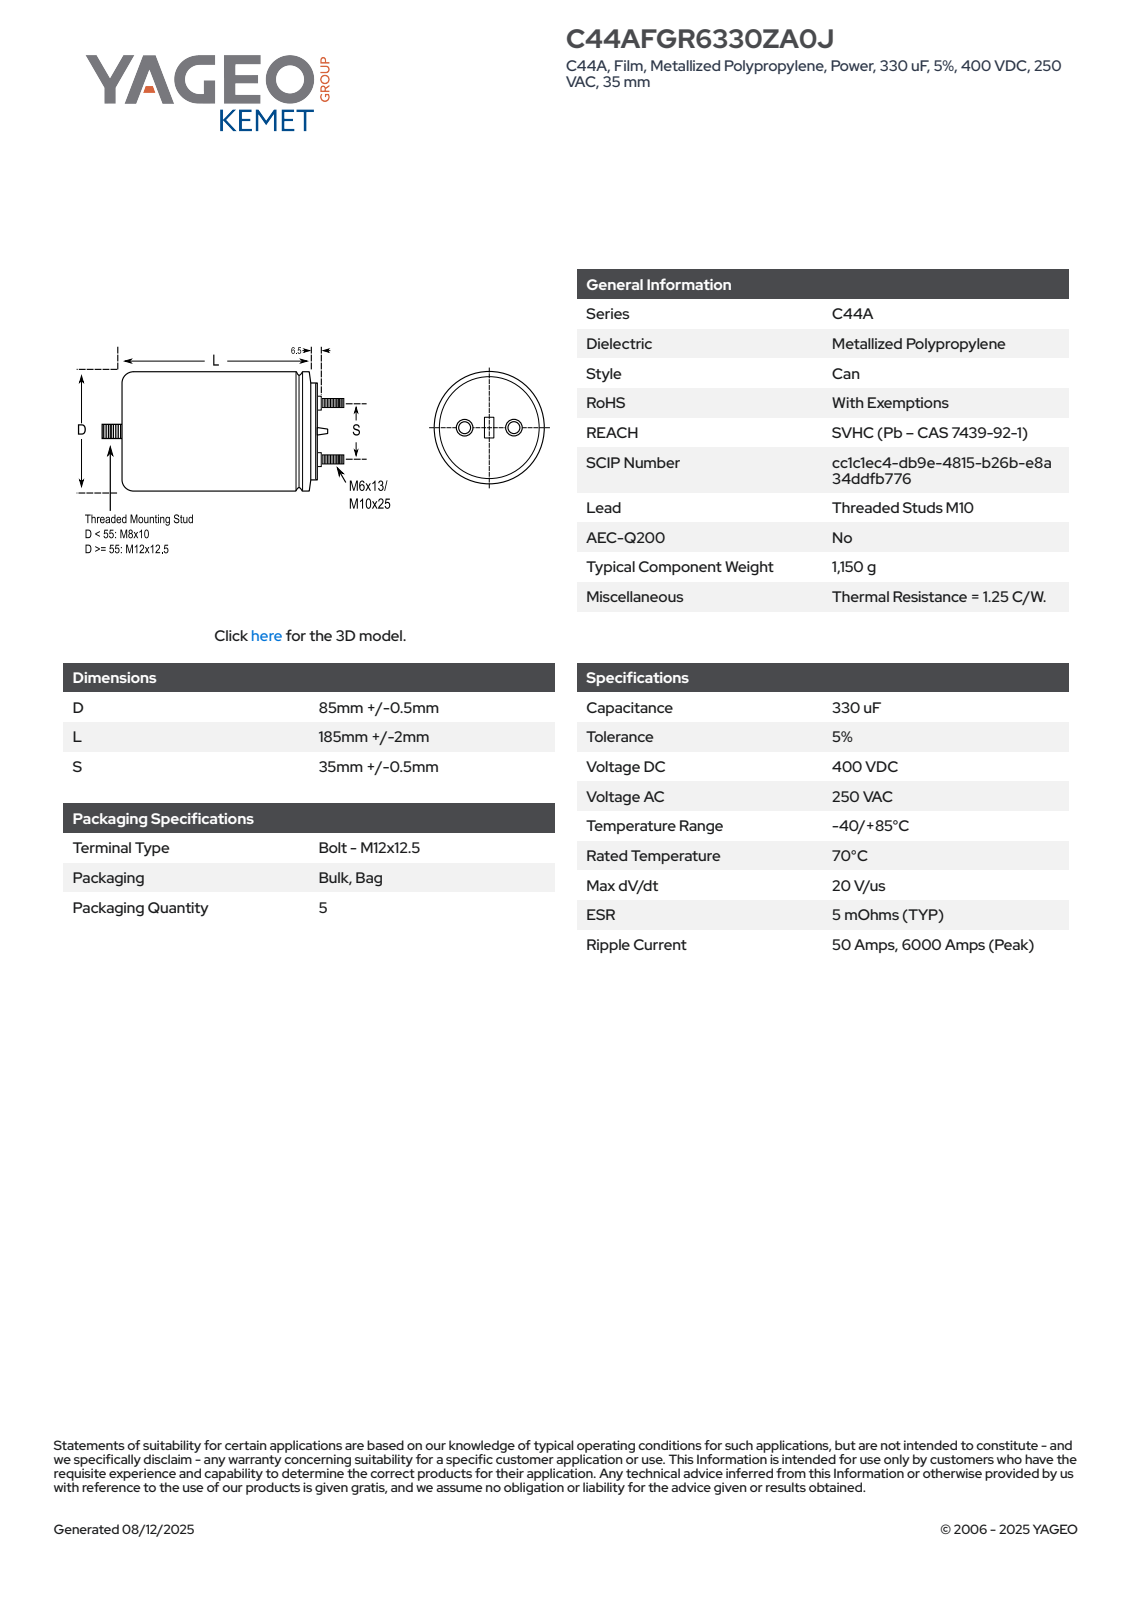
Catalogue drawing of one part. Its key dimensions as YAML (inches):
part_name: "CFP_C44A_85X185_D85.5L187S35"
step_written_by: "SolidWorks 2014 (AUTOMOTIVE_DESIGN)"
units: inches
bodies: {solids: 1, faces: 102, planar: 29, cylindrical: 34, other: 39}
overall_size: [8.622, 3.366, 3.366]
volume: 66.21
surface_area: 97.78
round_bosses_or_shafts:
  - {diameter: 0.354, count: 2}
  - {diameter: 0.236, count: 2}
  - {diameter: 3.366, count: 1}
  - {diameter: 2.64, count: 1}
  - {diameter: 0.472, count: 1}
partial_cylinders:
  - {radius: 1.683, count: 1}
face_to_face_distances: [7.559, 0.492, 8.051, 8.11, 7.618, 0.059, 8.622, 8.13, 0.571, 0.512]
